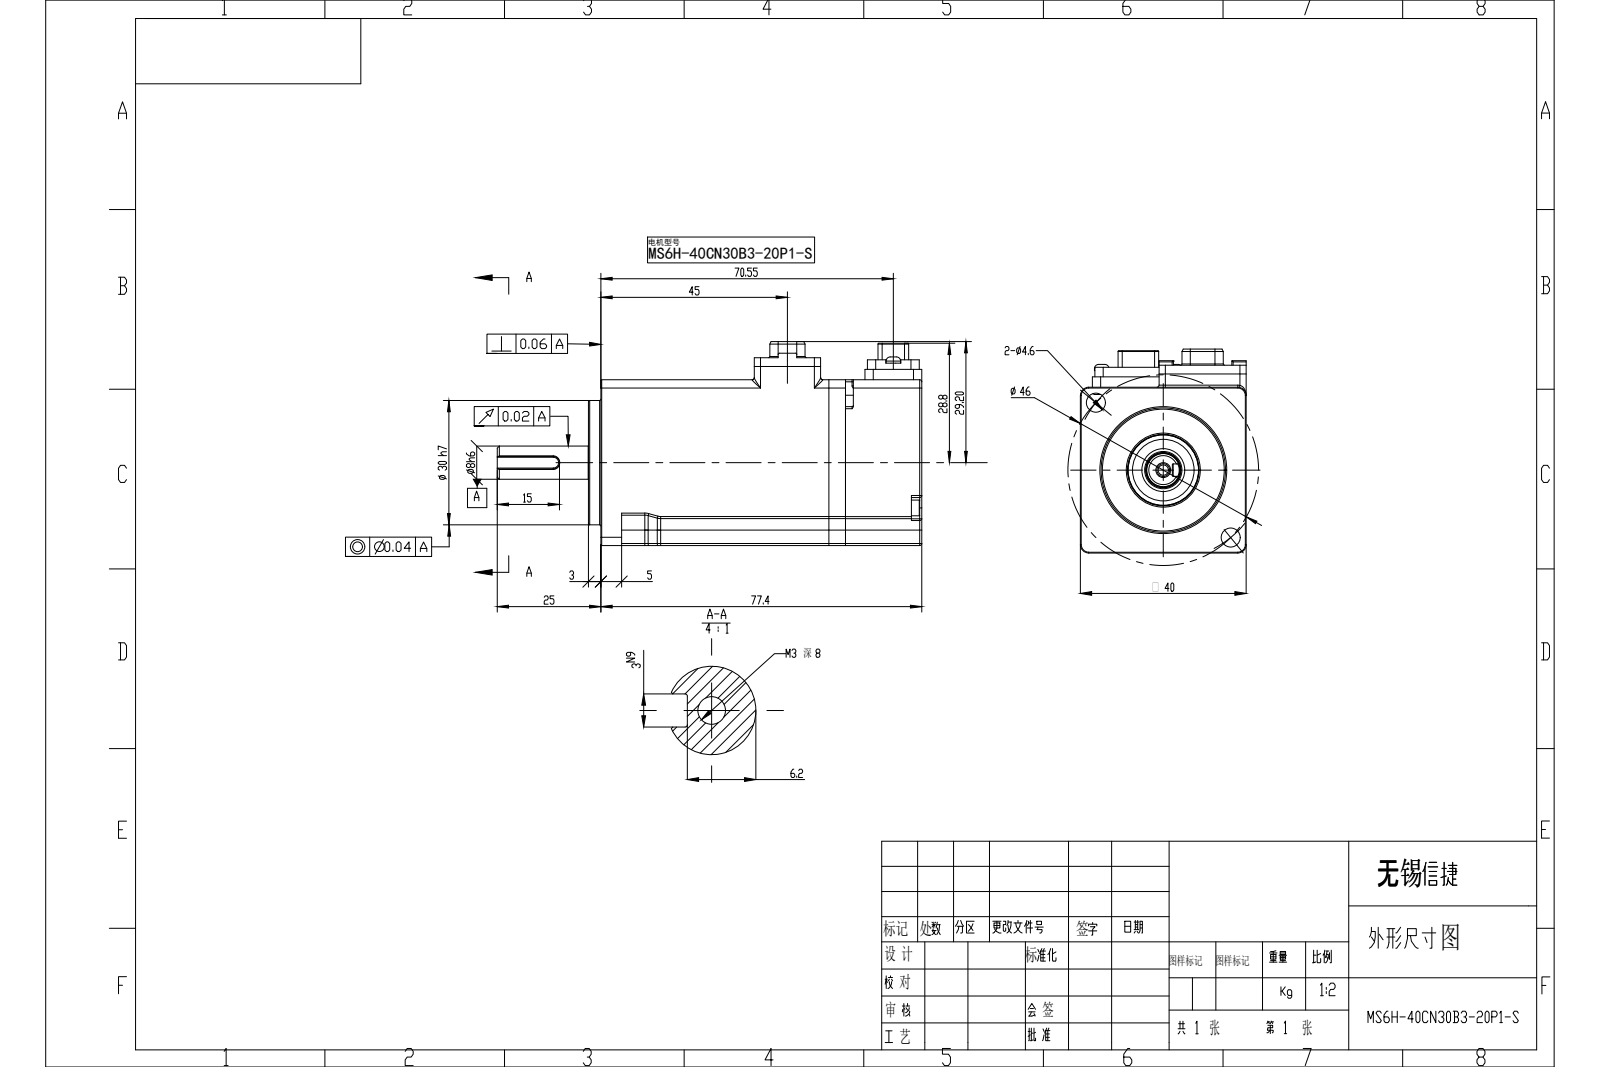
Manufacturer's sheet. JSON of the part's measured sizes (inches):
{"part_name": "MS6H-40CN30B3-20P1-S", "step_written_by": "SolidWorks 2022 (AUTOMOTIVE_DESIGN)", "units": "inches", "bodies": {"solids": 0, "faces": 648, "planar": 326, "cylindrical": 209, "other": 113}, "overall_size": [4.031, 1.937, 1.575], "round_holes": [[0.083, 8], [0.063, 2], [0.181, 2], [0.098, 1], [0.354, 1], [0.585, 1]], "round_bosses_or_shafts": [[0.15, 4], [0.138, 2], [1.181, 1], [0.669, 1], [0.407, 1], [0.335, 1], [0.315, 1]], "partial_cylinders_radius": [[0.02, 52], [0.008, 18], [0.012, 18], [0.079, 16], [0.118, 8], [0.059, 5], [0.039, 4], [0.098, 4]], "face_to_face_distances": [1.575, 0.256, 1.319, 3.047, 0.118, 0.724, 2.323, 0.157, 3.165, 2.441], "hole_center_spacings": [0.23, 0.708, 0.669, 0.315, 0.461, 0.654, 0.726, 0.813]}
